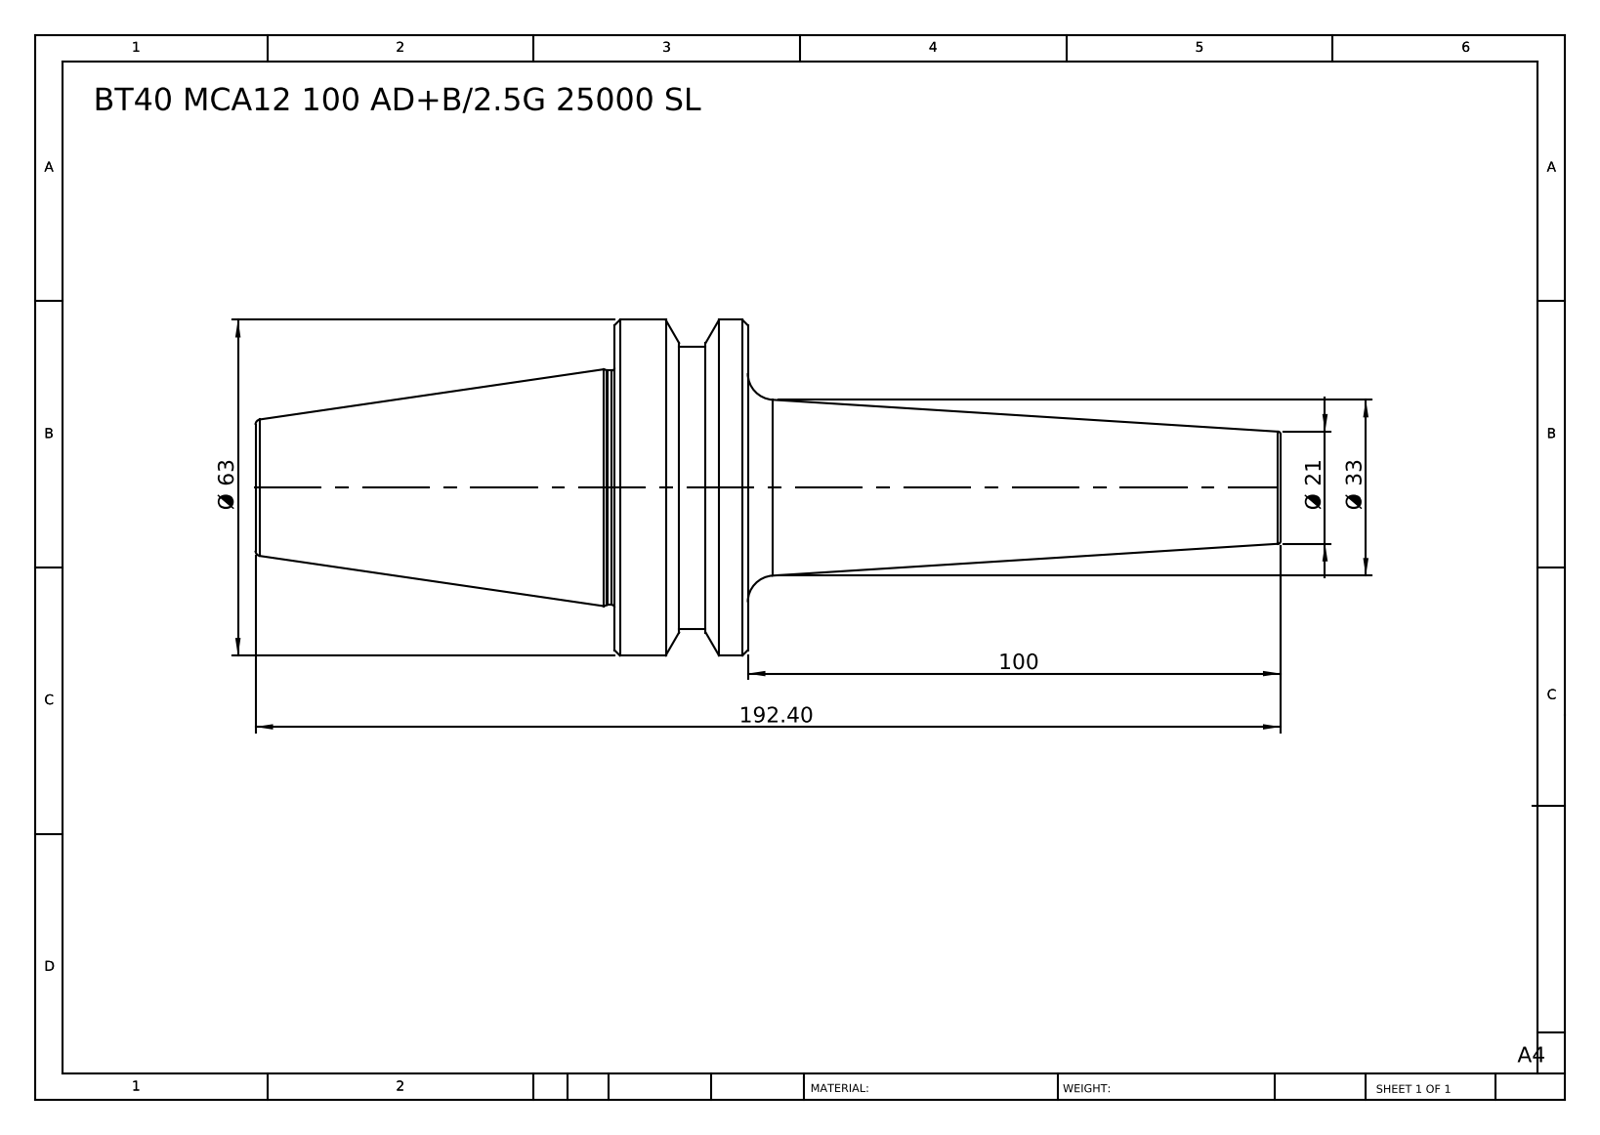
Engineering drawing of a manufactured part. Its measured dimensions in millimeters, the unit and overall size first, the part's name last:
Units: millimetres
Overall size (bounding box): 192.4 × 63 × 63
Round bosses / shafts (diameter × count): ⌀63 ×1, ⌀53 ×1, ⌀44 ×1
Main face-to-face distances: 25, 92.4, 67.4, 100, 125, 192.4, 112.9, 12.9, 12.1, 79.5
Volume: 198 411 mm³ · Surface area: 26 187 mm²
Bodies: 1 solid, 38 faces (6 planar, 8 cylindrical, 24 other)
Part name (STEP PRODUCT): BT40 MCA12 100 AD+B-2.5G 25000 SL
STEP written by: SolidWorks 2014 (CONFIG_CONTROL_DESIGN)
